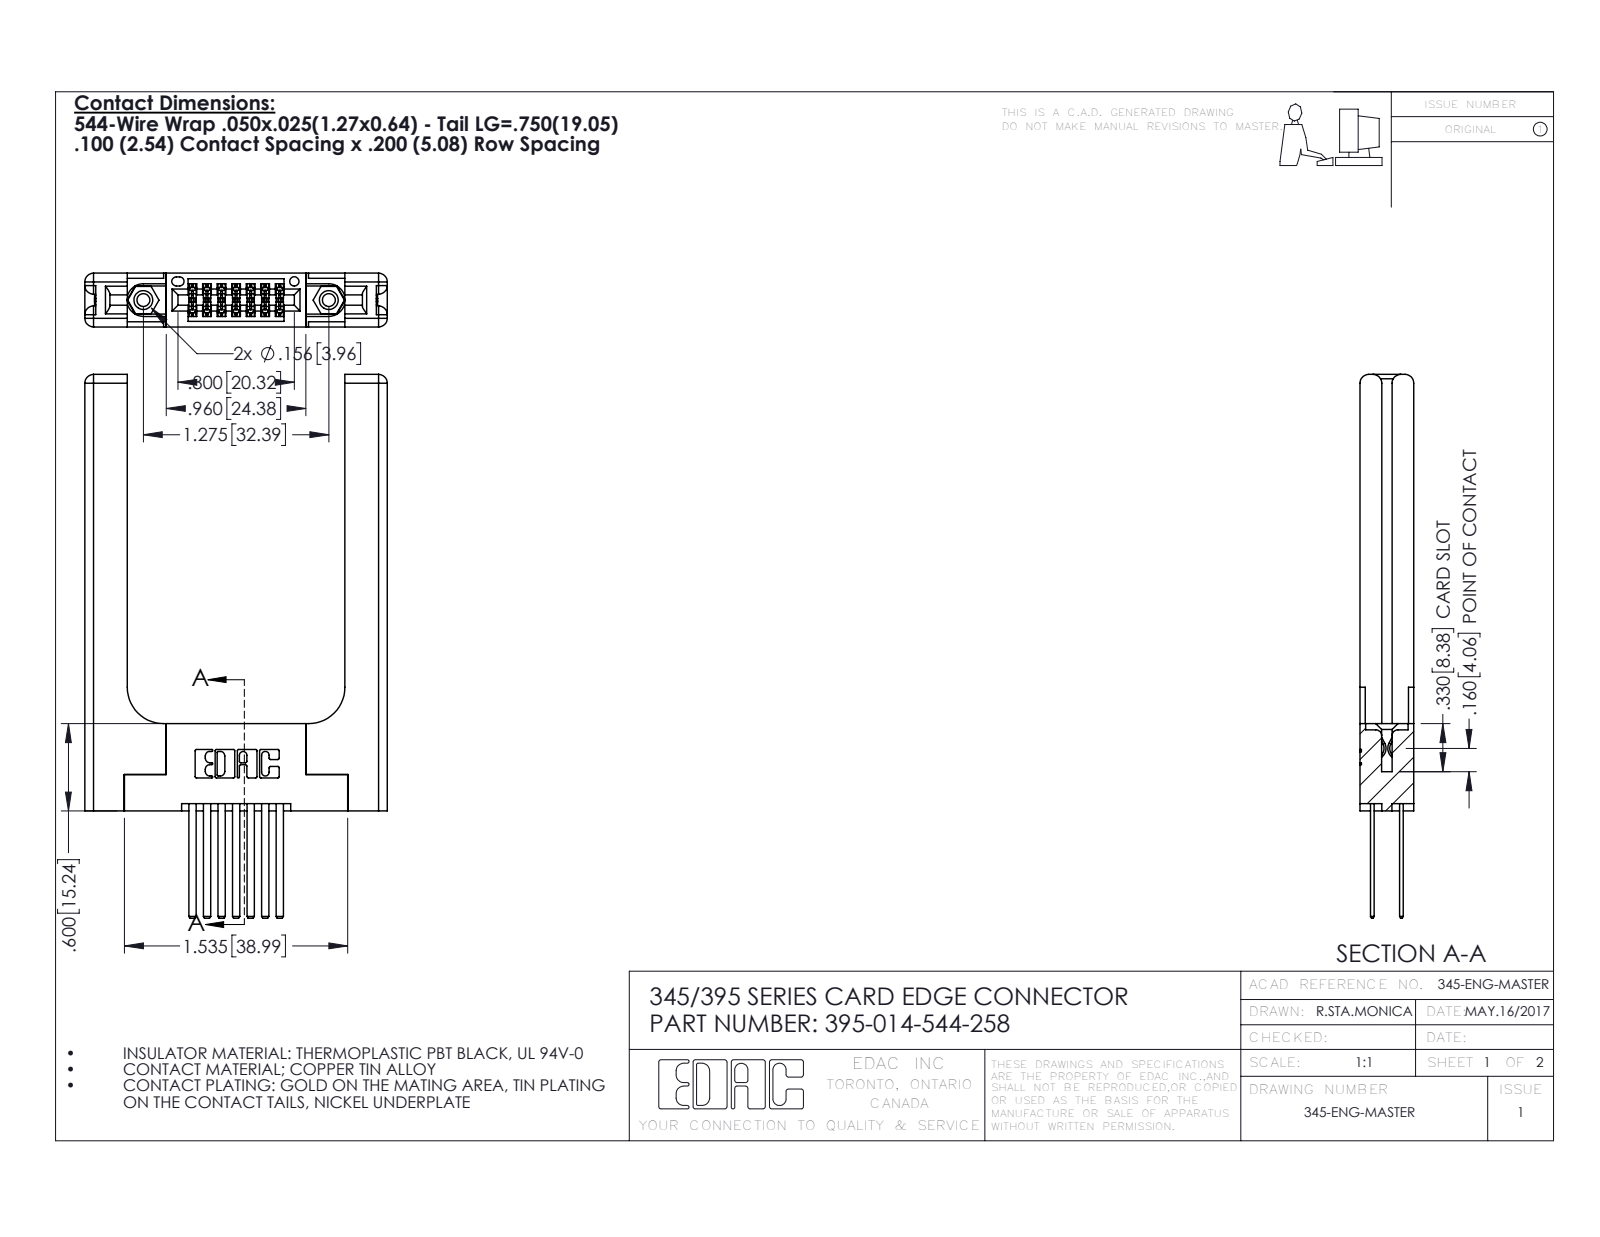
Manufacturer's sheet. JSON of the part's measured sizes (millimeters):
{"part_name": "395-014-544-258; 345-220-058_345-220-058; 345 Part_Flush Mounting Lugs - 0.156 Dia-TH; 345-250-001_345-250-001-102 (+1 more)", "step_written_by": "SolidWorks 2016 (CONFIG_CONTROL_DESIGN)", "units": "millimeters", "bodies": {"solids": 19, "faces": 998, "planar": 634, "cylindrical": 304, "other": 60}, "overall_size": [94.9, 52.8, 9.4], "volume_mm3": 13500, "surface_area_mm2": 12350, "round_holes": [[2.3, 2], [3.2, 2], [4, 2], [1.6, 1]], "round_bosses_or_shafts": [[3.9, 2]], "partial_cylinders_radius": [[0.3, 22], [0.2, 21], [1.5, 16], [0.2, 6], [0.8, 6], [0.7, 3], [0.4, 2], [0.5, 2]], "face_to_face_distances": [9.4, 1.8, 7.6, 2, 3.8, 3.8, 5.6, 5.1, 2.5, 6.9], "hole_center_spacings": [6.9, 26.5, 32.4]}
